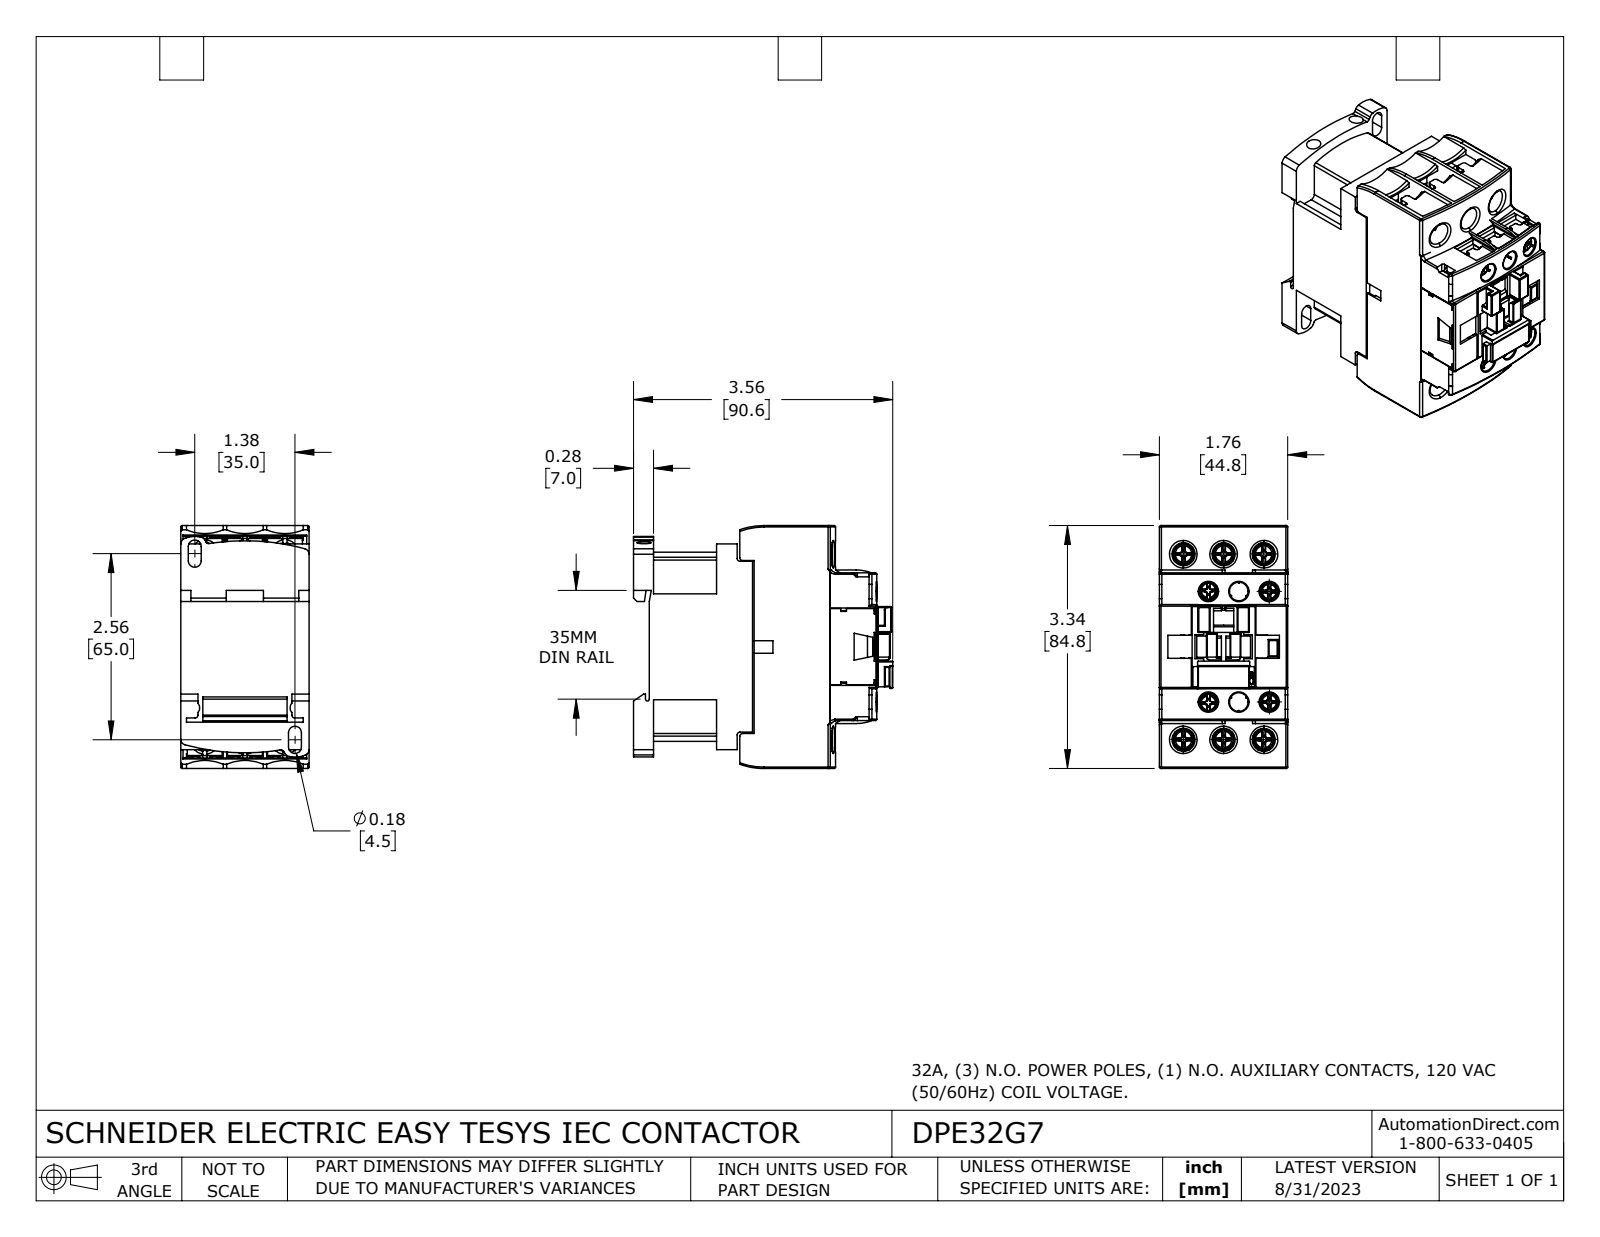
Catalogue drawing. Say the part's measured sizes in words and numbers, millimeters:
The part is named "DPE32G7". Its 3-D file was written by "SolidWorks 2021 (CONFIG_CONTROL_DESIGN)". It is 16 solids with 2674 faces: 1724 planar, 584 cylindrical and 366 other. Overall it measures 90.6 by 84.8 by 44.8 millimeters. Its volume is 205 800 cubic millimeters and its surface area 64 770 square millimeters. Round holes: 6 of diameter 6.5, 6 of diameter 8, 2 of diameter 5. Round bosses or shafts: 8 of diameter 4, 6 of diameter 3.2, 4 of diameter 3.5, 4 of diameter 3.4, 4 of diameter 2.7, 3 of diameter 10. Partial cylindrical surfaces (rounded edges, fillets, slot ends): 58 of radius 0.3, 36 of radius 0.2, 36 of radius 1, 34 of radius 0.5, 18 of radius 16, 17 of radius 0.2, 9 of radius 2, 8 of radius 0.8. The main face-to-face distances are 44.8, 14, 0.6, 1.5, 27.7, 27.1, 1.2, 0.8, 35.1, 36. The hole center spacings are 10.6, 14, 40, 66.3, 38.6, 64.8, 14, 14.2.
